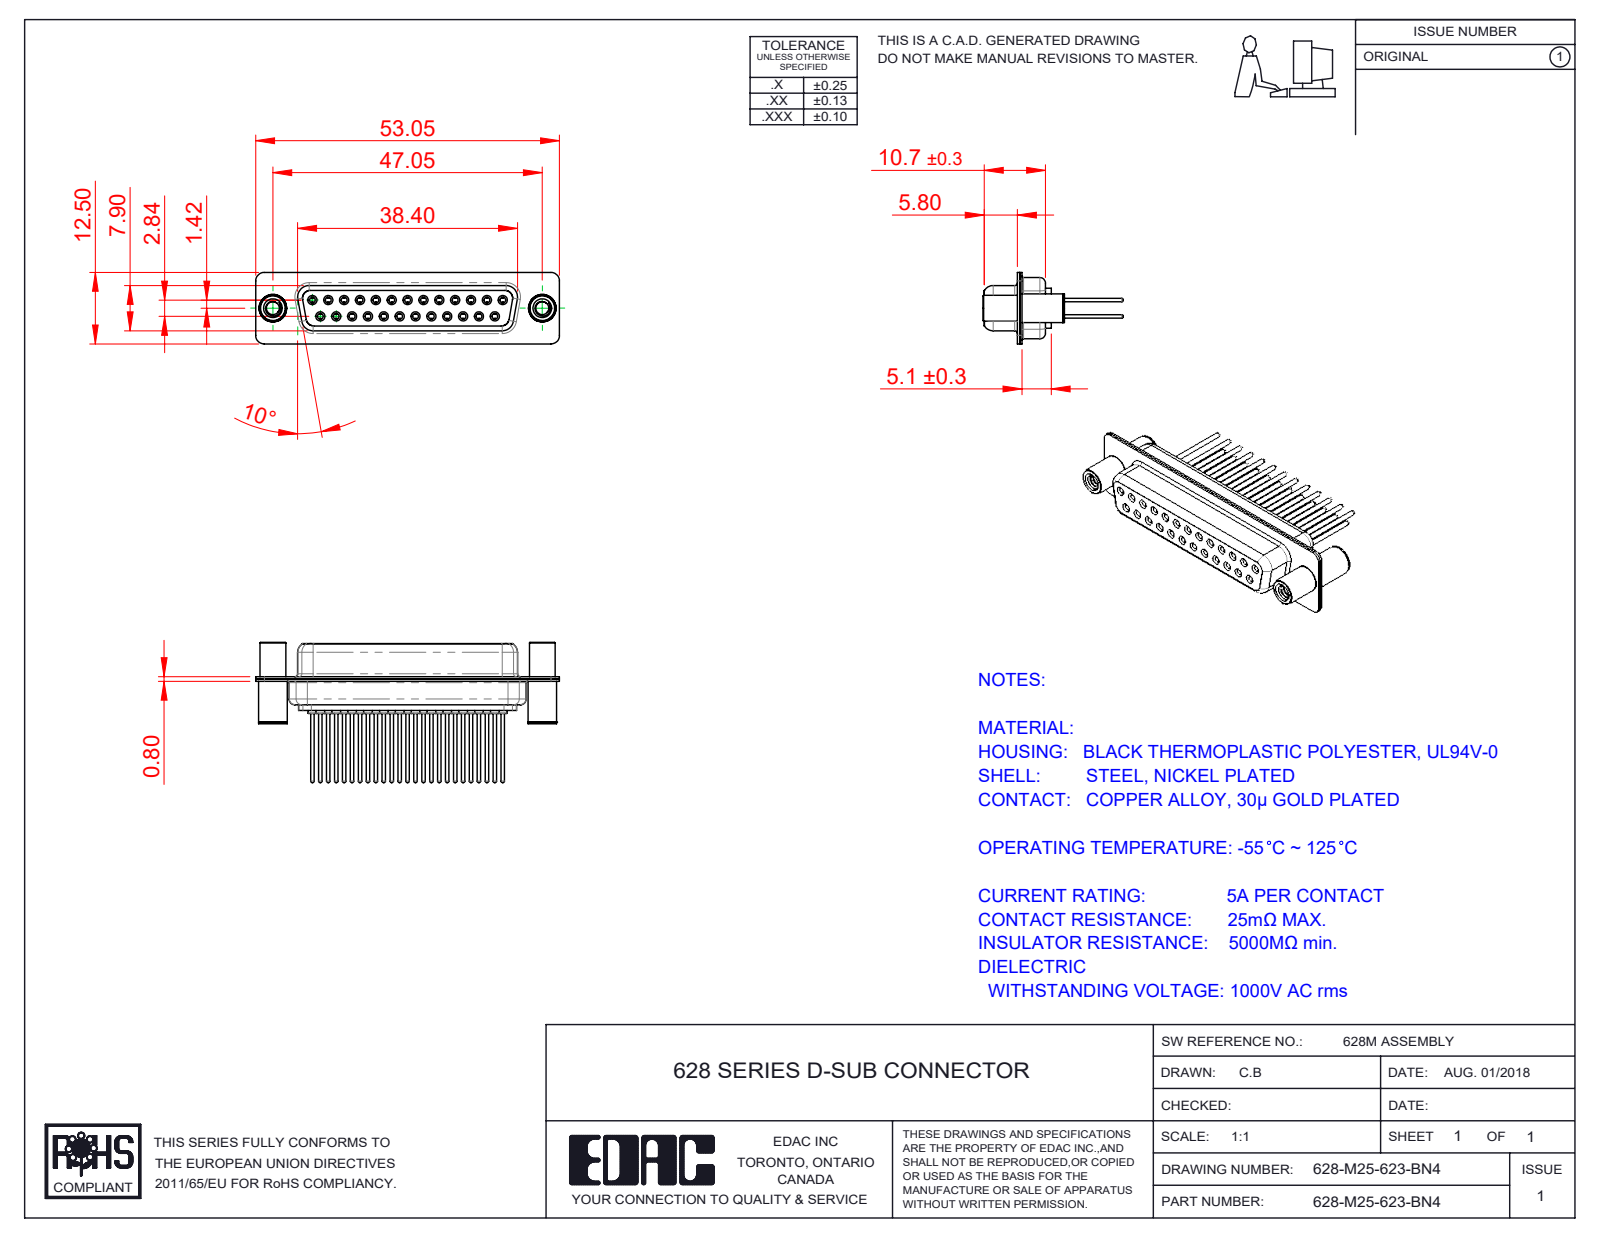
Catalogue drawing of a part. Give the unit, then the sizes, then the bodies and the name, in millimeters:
Units: millimetres
Overall size (bounding box): 53.05 × 24.47 × 12.5
Round holes (diameter × count): ⌀1 ×25, ⌀1.1 ×25, ⌀1.7 ×25, ⌀1.8 ×25, ⌀2 ×25, ⌀2.26 ×2, ⌀3.26 ×2, ⌀4 ×2, ⌀4.8 ×2
Round bosses / shafts (diameter × count): ⌀2.2 ×25, ⌀1.6 ×25, ⌀1.5 ×25, ⌀0.6 ×25, ⌀5 ×2, ⌀4.9 ×2, ⌀4.5 ×2
Partial cylindrical surfaces — rounded edges, fillets, slot ends (radius × count): R1.5 ×16, R2 ×12, R1.35 ×8, R1.6 ×8, R0.25 ×4, R0.5 ×4, R0.6 ×4, R0.65 ×4
Main face-to-face distances: 0.4, 1.4, 0.45, 8.45, 8.9, 1.8, 6.2, 7.05, 1, 1.85
Hole centre spacings: 3.16, 2.77, 5.54, 8.31, 11.08, 13.85, 5.04, 7.49
Volume: 4 074 mm³ · Surface area: 9 990 mm²
Bodies: 30 solids, 1740 faces (448 planar, 664 cylindrical, 628 other)
Part name (STEP PRODUCT): 628M Contact Row 2_23; 628M 4-40 Threaded Standoff and Board Spacer; 628M Shell Rear_25 Contacts; 628M Shell Front_25 Contacts (+3 more)
STEP written by: SolidWorks 2020 (CONFIG_CONTROL_DESIGN)
